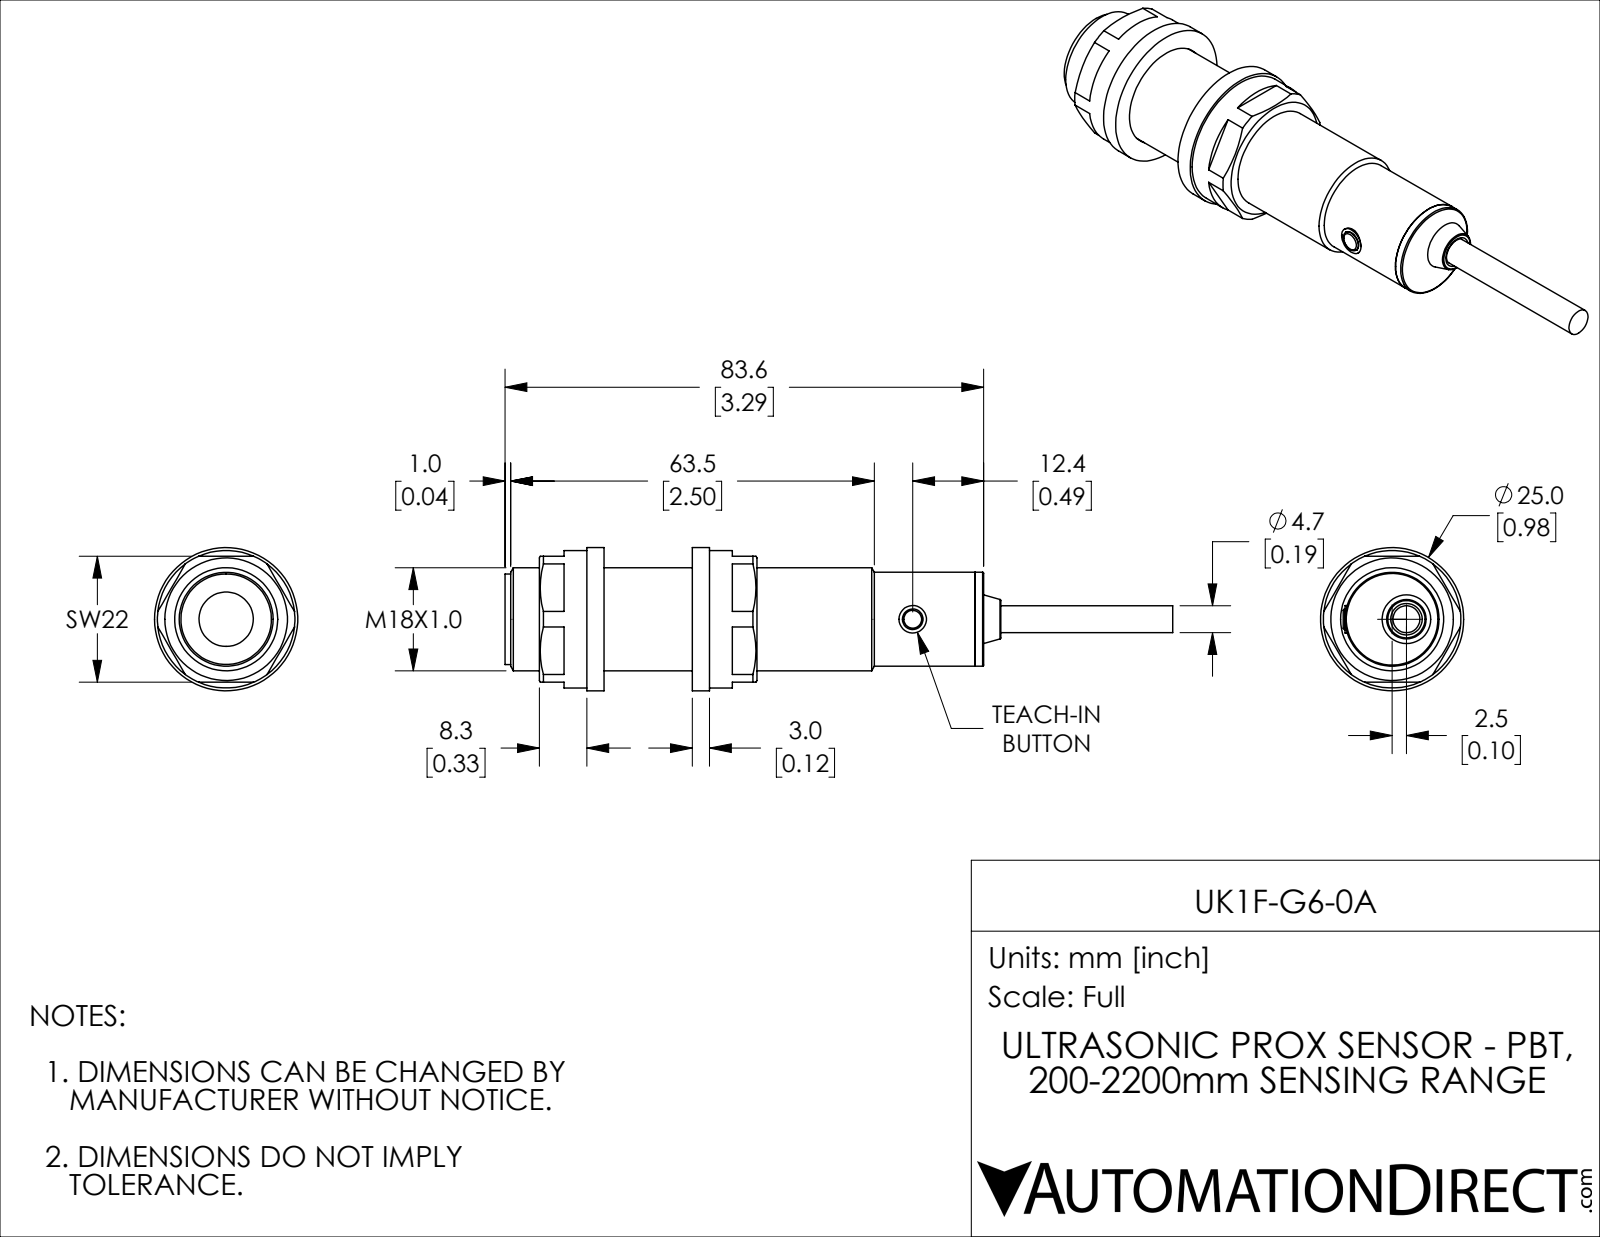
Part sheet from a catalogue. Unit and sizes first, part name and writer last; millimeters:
Units: millimetres
Overall size (bounding box): 116.6 × 25 × 25
Round holes (diameter × count): ⌀4.7 ×2, ⌀3.6 ×1, ⌀9.5 ×1, ⌀18 ×1, ⌀18.2 ×1
Round bosses / shafts (diameter × count): ⌀25 ×1, ⌀24 ×1, ⌀16.4 ×1, ⌀15.8 ×1, ⌀5.4 ×1, ⌀4.8 ×1
Main face-to-face distances: 3, 18.4, 21.4, 67.8, 46.4, 13.3, 34.7, 81.1, 16.3, 64.8
Hole centre spacings: 2.5
Volume: 25 220 mm³ · Surface area: 11 419 mm²
Bodies: 10 solids, 107 faces (49 planar, 40 cylindrical, 18 other)
Part name (STEP PRODUCT): UK1F-G6-0A
STEP written by: SolidWorks 2018 (AUTOMOTIVE_DESIGN)
